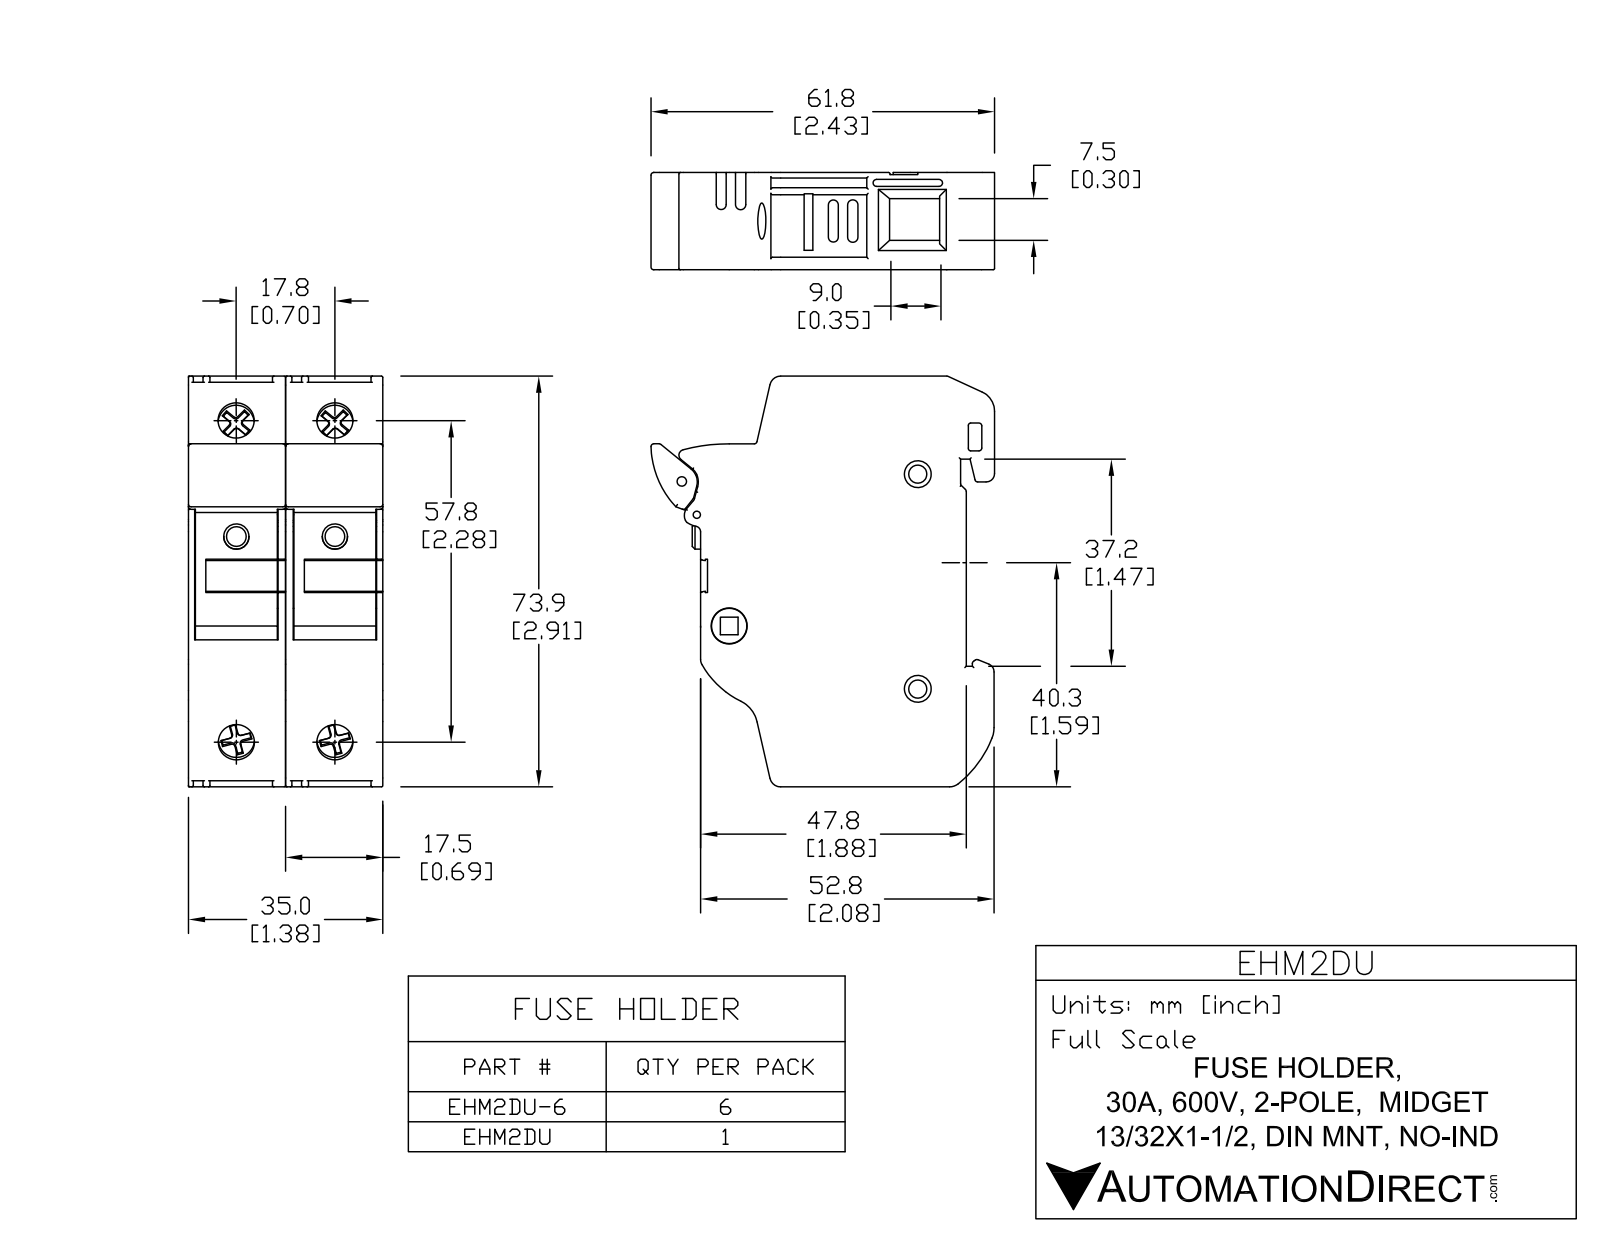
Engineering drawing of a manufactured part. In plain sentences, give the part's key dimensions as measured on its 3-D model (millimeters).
The part is named "EHM2DU". Its 3-D file was written by "SolidWorks 2017 (AUTOMOTIVE_DESIGN)". It is 2 solids with 1166 faces: 490 planar, 388 cylindrical and 288 other. Overall it measures 73.88 by 61.82 by 35 millimeters. Its volume is 105 443 cubic millimeters and its surface area 39 091 square millimeters. Round holes: 4 of diameter 6.5, 2 of diameter 3.25, 2 of diameter 4.83, 1 of diameter 1.3, 1 of diameter 1.7, 1 of diameter 6.48. Round bosses or shafts: 1 of diameter 6.35. Partial cylindrical surfaces (rounded edges, fillets, slot ends): 134 of radius 0.25, 11 of radius 0.5, 10 of radius 2, 9 of radius 0.51, 8 of radius 0.62, 7 of radius 1, 6 of radius 0.89, 6 of radius 0.92. The main face-to-face distances are 17.5, 35, 1.25, 1.58, 16.25, 27.51, 29.09, 22.94, 24.71, 0.4. The hole center spacings are 17.5, 6.58, 20.83, 27.36, 35.77, 35.79, 38.61, 38.66.
